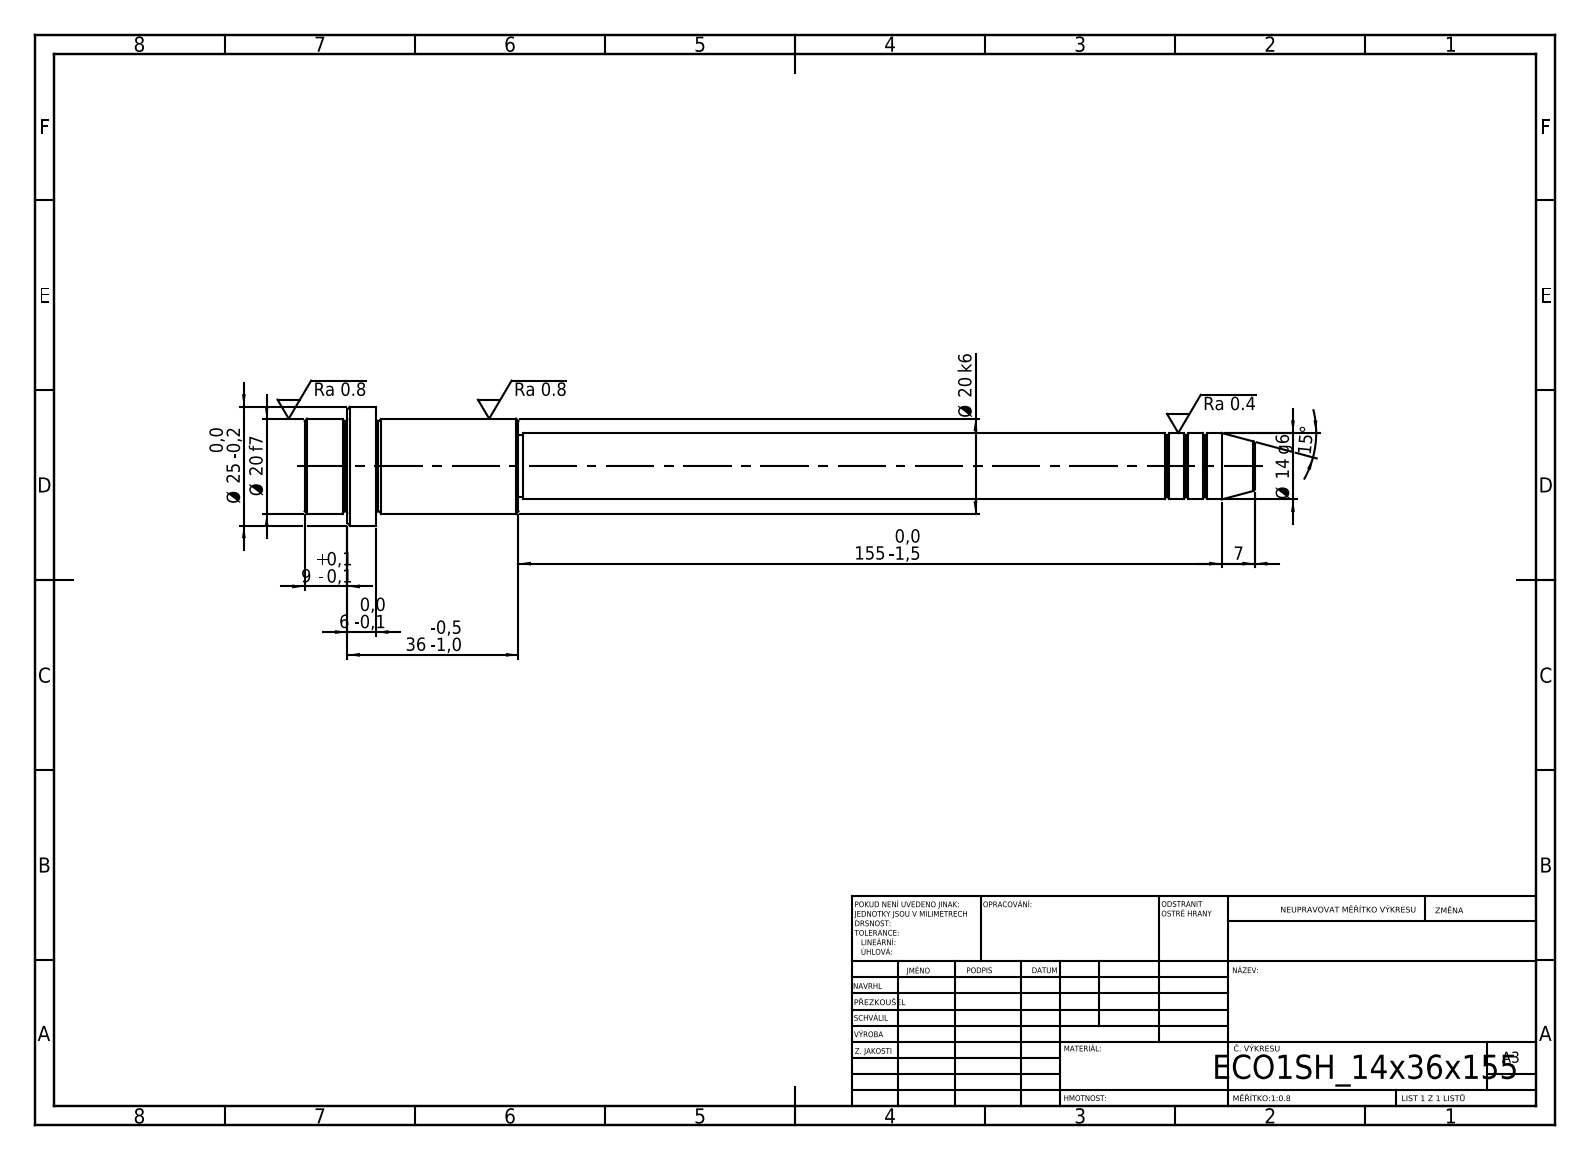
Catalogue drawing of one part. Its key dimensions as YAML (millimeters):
step_written_by: "SolidWorks 2019 (CONFIG_CONTROL_DESIGN)"
units: millimeters
bodies: {solids: 1, faces: 52, planar: 6, cylindrical: 16, other: 30}
overall_size: [200, 25, 25]
volume: 38649
surface_area: 10724
round_bosses_or_shafts:
  - {diameter: 25, count: 1}
  - {diameter: 20, count: 1}
  - {diameter: 14, count: 1}
  - {diameter: 13, count: 1}
face_to_face_distances: [15, 30, 45, 36, 6, 9, 155, 185, 191, 200]
